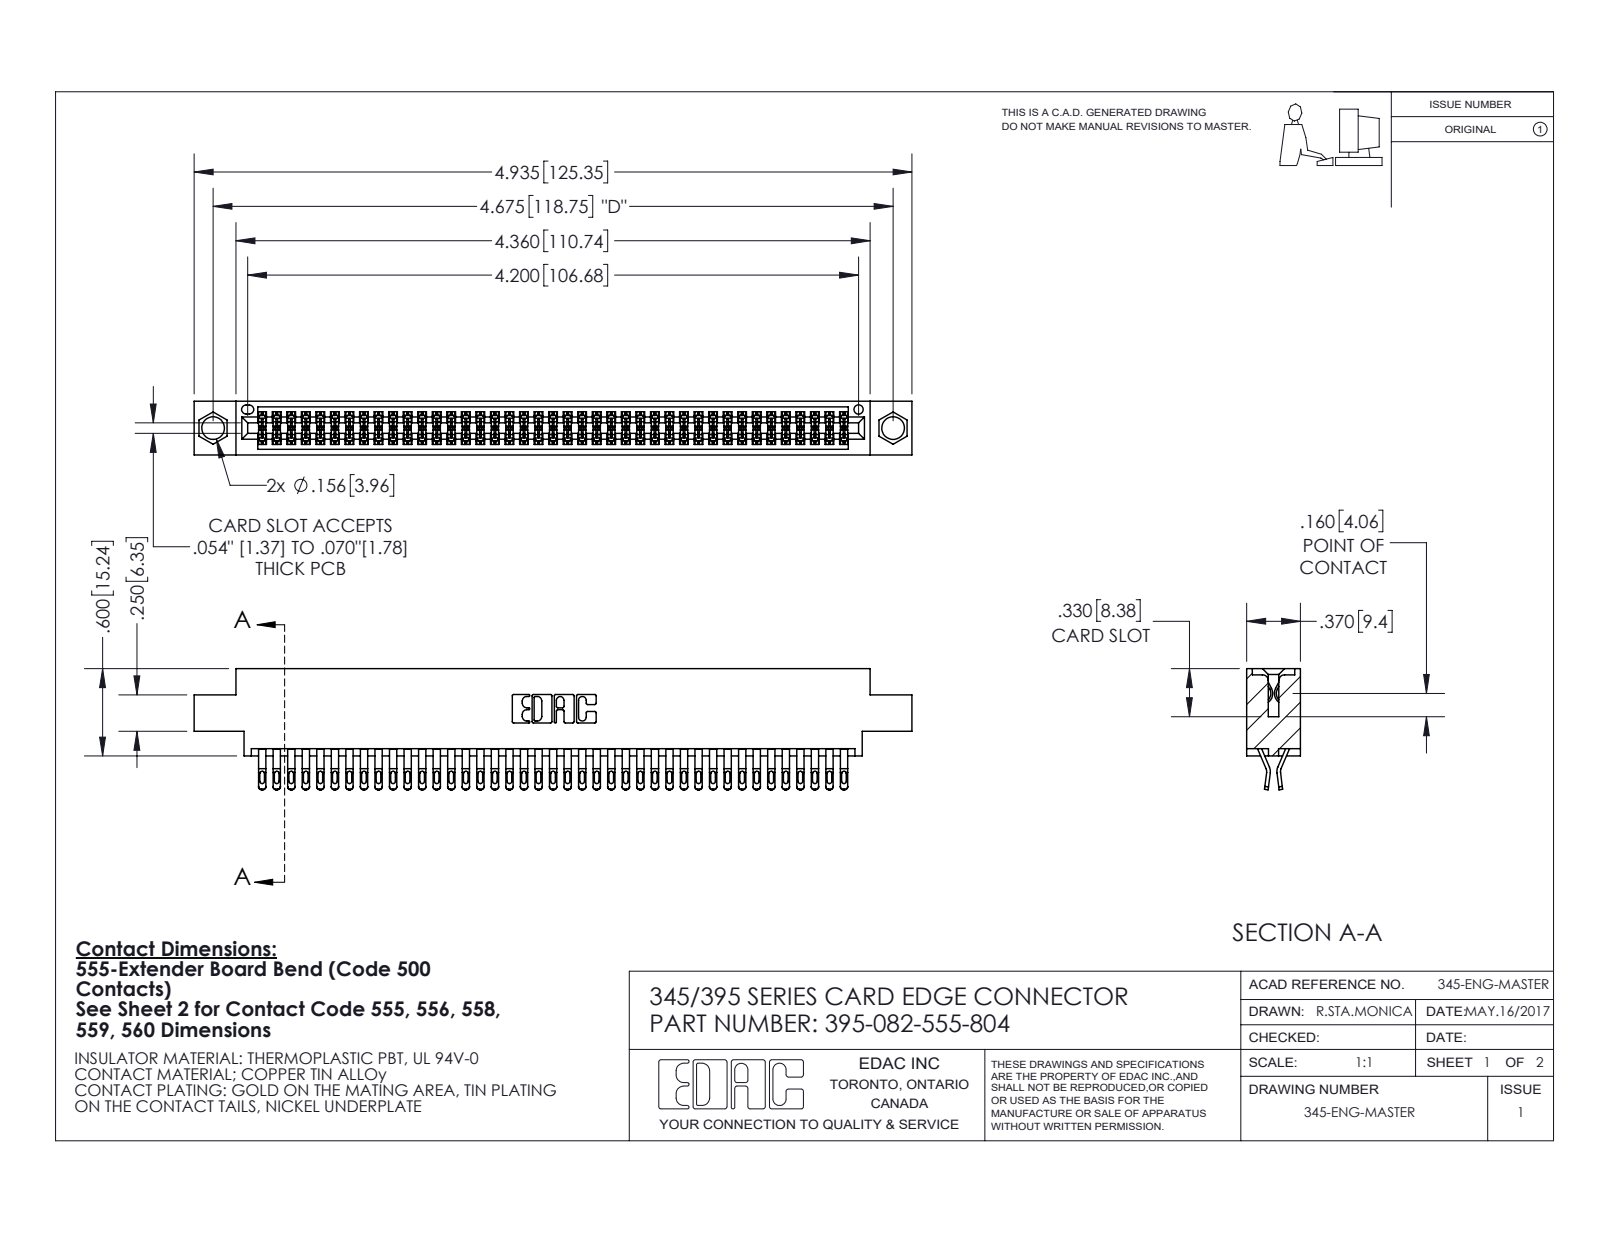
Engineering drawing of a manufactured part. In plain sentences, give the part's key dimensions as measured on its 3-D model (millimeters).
The part is named "395-082-555-804; 345 Part_0.170 Offset - 0.156 Dia-TI; 345-292-001_555 Tail". Its 3-D file was written by "SolidWorks 2020 (CONFIG_CONTROL_DESIGN)". It is 83 solids with 4736 faces: 2640 planar, 2096 cylindrical and 0 other. Overall it measures 125.3 by 21.1 by 9.4 millimeters. Its volume is 12 200 cubic millimeters and its surface area 18 810 square millimeters. Round holes: 2 of diameter 4, 1 of diameter 1.6. Partial cylindrical surfaces (rounded edges, fillets, slot ends): 205 of radius 0.4, 164 of radius 0.2, 164 of radius 0.5, 22 of radius 0.3, 6 of radius 0.2, 6 of radius 0.8, 3 of radius 0.7, 2 of radius 0.3. The main face-to-face distances are 1.8, 7.6, 9.4, 0.6, 5.1, 2.5, 6.9, 5.7, 4.4, 3.8. The hole center spacings are 6.9, 112.8, 118.7.
